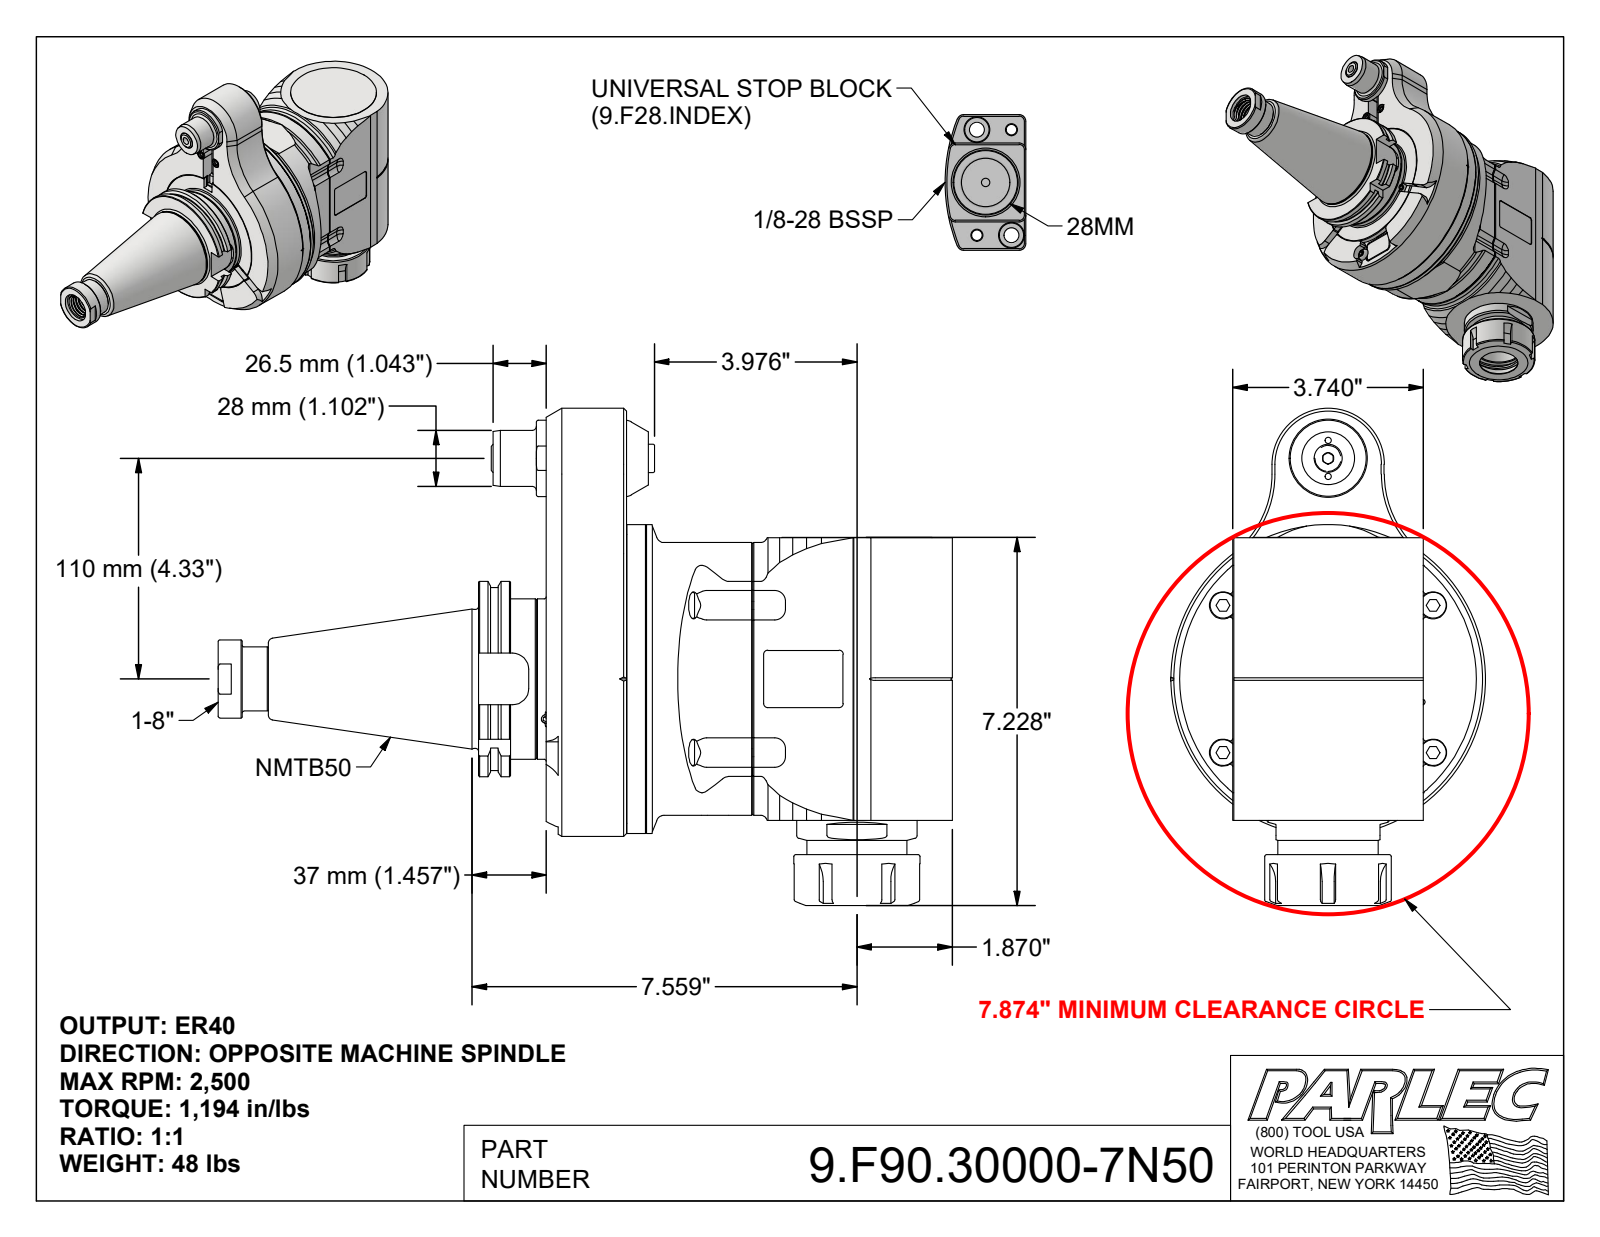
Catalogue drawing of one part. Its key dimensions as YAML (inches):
part_name: "9.F90.30000-7N50; 9_GA3_251_2 (EVO, Type 3, NMTB (DIN20; 9_F90_30000"
step_written_by: "Autodesk Inventor 2025 (AUTOMOTIVE_DESIGN)"
units: inches
bodies: {solids: 8, faces: 855, planar: 367, cylindrical: 230, other: 258}
overall_size: [14.419, 9.764, 6.181]
volume: 209.6
surface_area: 515.5
round_holes:
  - {diameter: 0.266, count: 4}
  - {diameter: 0.335, count: 4}
  - {diameter: 0.531, count: 4}
  - {diameter: 0.197, count: 3}
  - {diameter: 0.126, count: 2}
  - {diameter: 0.165, count: 2}
  - {diameter: 0.209, count: 2}
  - {diameter: 0.315, count: 2}
  - {diameter: 0.098, count: 1}
  - {diameter: 0.256, count: 1}
  - {diameter: 0.472, count: 1}
  - {diameter: 0.492, count: 1}
round_bosses_or_shafts:
  - {diameter: 0.512, count: 4}
  - {diameter: 0.315, count: 4}
  - {diameter: 0.098, count: 2}
  - {diameter: 6.063, count: 1}
  - {diameter: 5.669, count: 1}
  - {diameter: 4.634, count: 1}
  - {diameter: 4.398, count: 1}
  - {diameter: 3.593, count: 1}
partial_cylinders:
  - {radius: 0.079, count: 12}
  - {radius: 0.276, count: 12}
  - {radius: 0.591, count: 7}
  - {radius: 0.118, count: 6}
  - {radius: 0.039, count: 4}
  - {radius: 0.157, count: 4}
  - {radius: 0.197, count: 4}
  - {radius: 0.394, count: 4}
face_to_face_distances: [1.378, 0.197, 1.181, 0.768, 0.236, 0.61, 0.571, 3.74, 0.315, 0.039]
hole_center_spacings: [2.52, 2.327, 3.563, 4.806, 5.039, 0.354, 0.622, 0.709]
